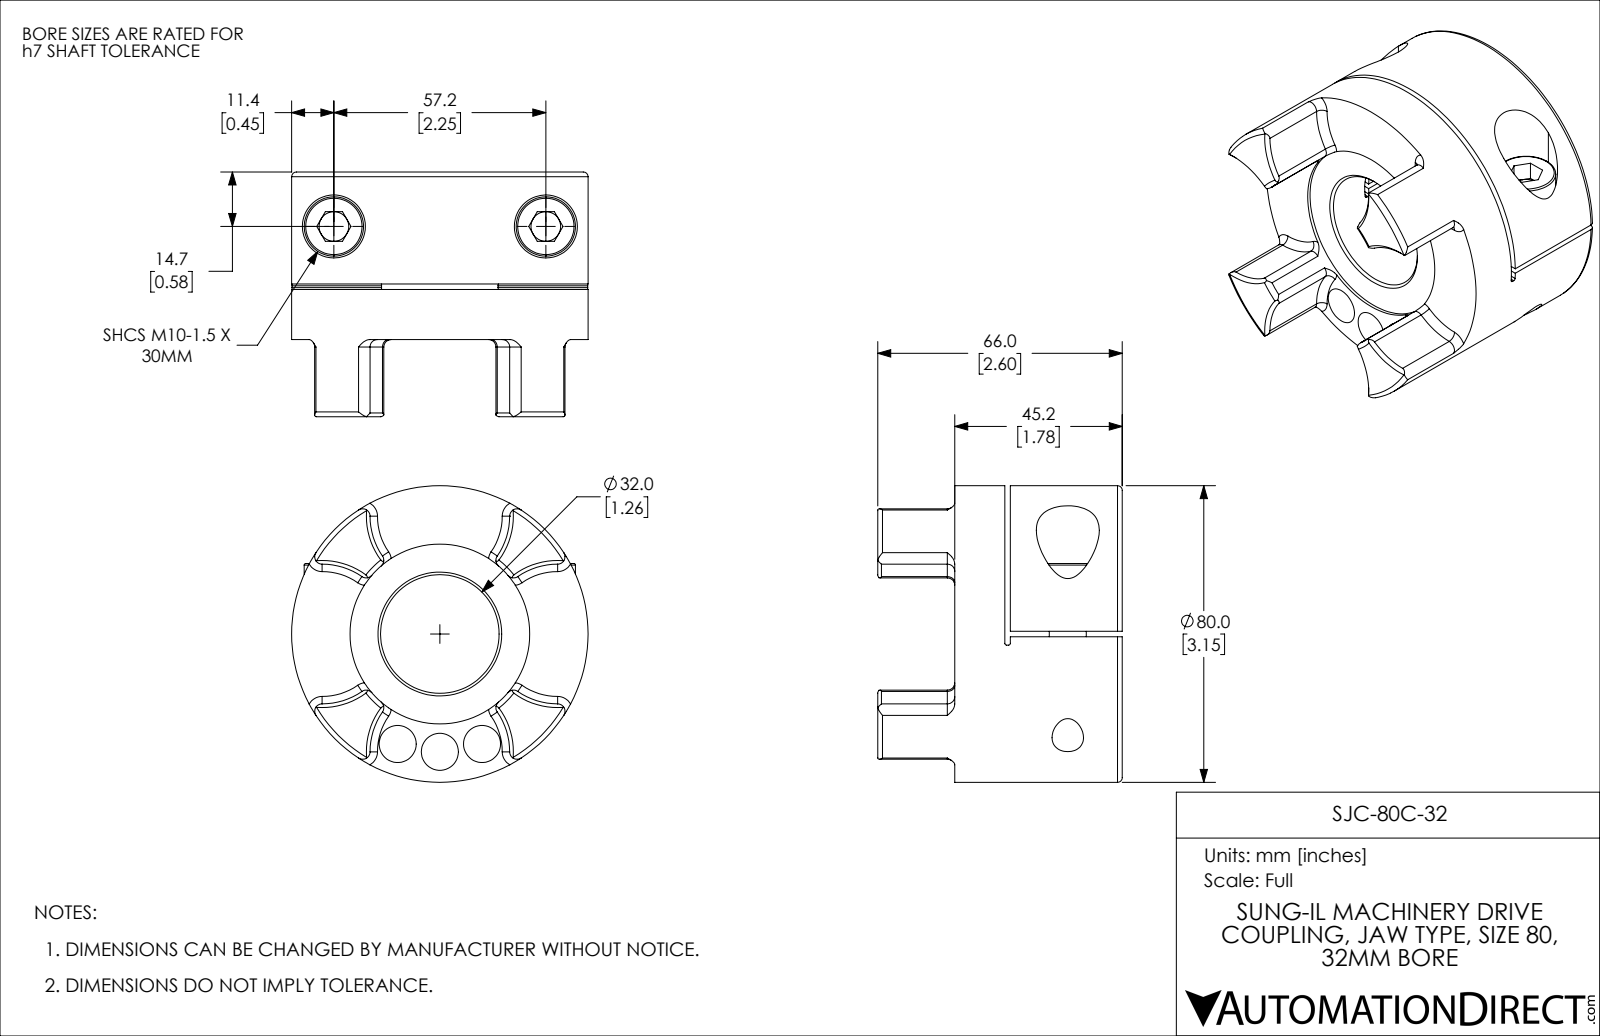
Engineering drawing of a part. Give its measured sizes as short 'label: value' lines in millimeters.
name: SJC-80C-32
written by: SolidWorks 2021 (CONFIG_CONTROL_DESIGN)
unit: mm
bodies: 4 solids, 217 faces (53 planar, 78 cylindrical, 86 other)
size: 80 × 80 × 66
volume: 191 911 mm³; area: 44 180 mm²
holes: 3× ⌀10, 2× ⌀8, 2× ⌀8.5, 2× ⌀10.5, 2× ⌀17, 1× ⌀32, 1× ⌀48.5
bosses: 2× ⌀16, 2× ⌀10, 1× ⌀80
rounds: 16× R2, 4× R18.84, 2× R0.5
face distances: 1.5, 31.7, 30.2, 13.5, 15, 45.2, 0.9, 12.6, 14.1, 44.3
hole spacings: 31.77, 11.58, 22.78, 57.2
